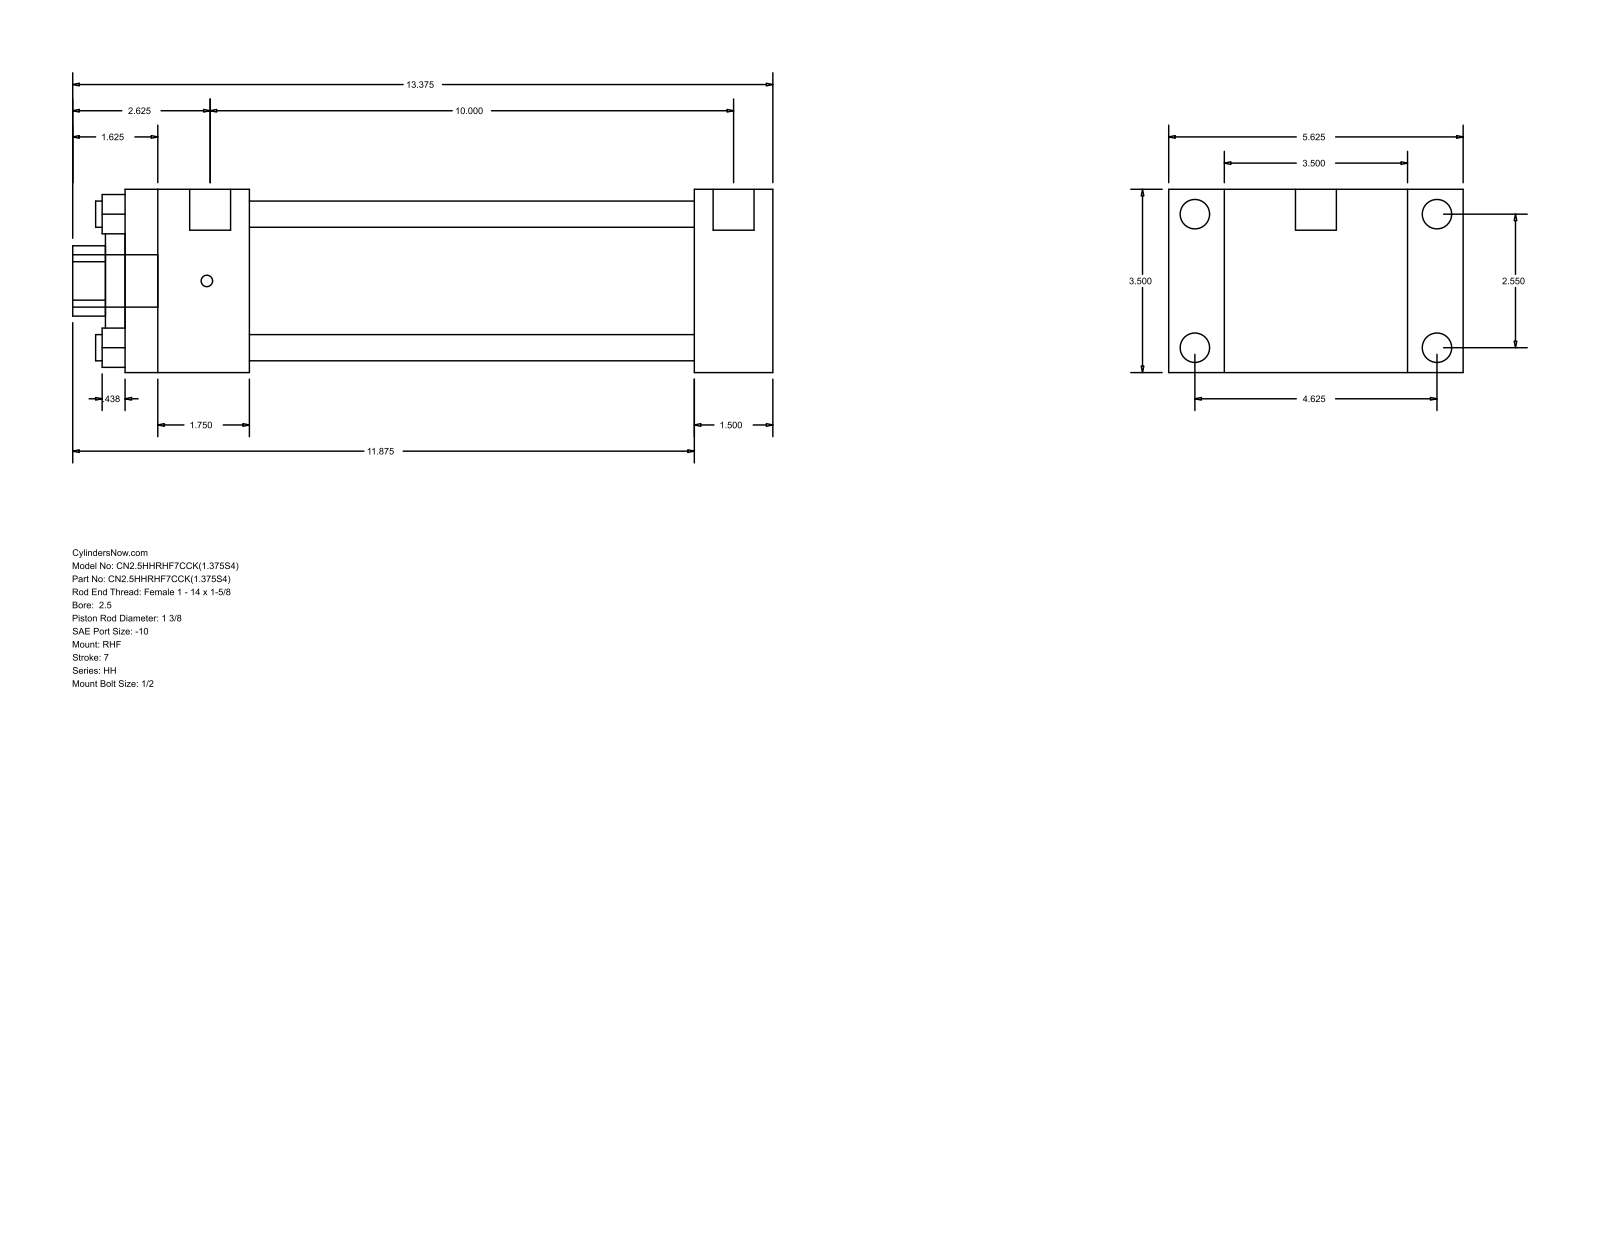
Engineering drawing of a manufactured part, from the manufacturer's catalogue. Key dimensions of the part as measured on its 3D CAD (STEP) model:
Part name (STEP PRODUCT): HH_RHF__0250_1.375
STEP written by: GSSL Pune (CONFIG_CONTROL_DESIGN)
Units: millimetres
Bodies: 0 solids, 88 faces (60 planar, 28 cylindrical, 0 other)
Overall size (bounding box): 339.73 × 142.88 × 88.9
Round holes (diameter × count): ⌀12.7 ×4, ⌀34.92 ×1, ⌀50.8 ×1, ⌀73.03 ×1
Round bosses / shafts (diameter × count): ⌀14.3 ×4, ⌀5.56 ×4, ⌀19.84 ×2, ⌀25.4 ×1
Partial cylindrical surfaces — rounded edges, fillets, slot ends (radius × count): R17.06 ×1
Main face-to-face distances: 88.9, 38.11, 26.99, 115.89, 276.22, 314.33, 142.88, 60.32, 215.9, 254.01
Hole centre spacings: 45.79, 64.76, 91.58
